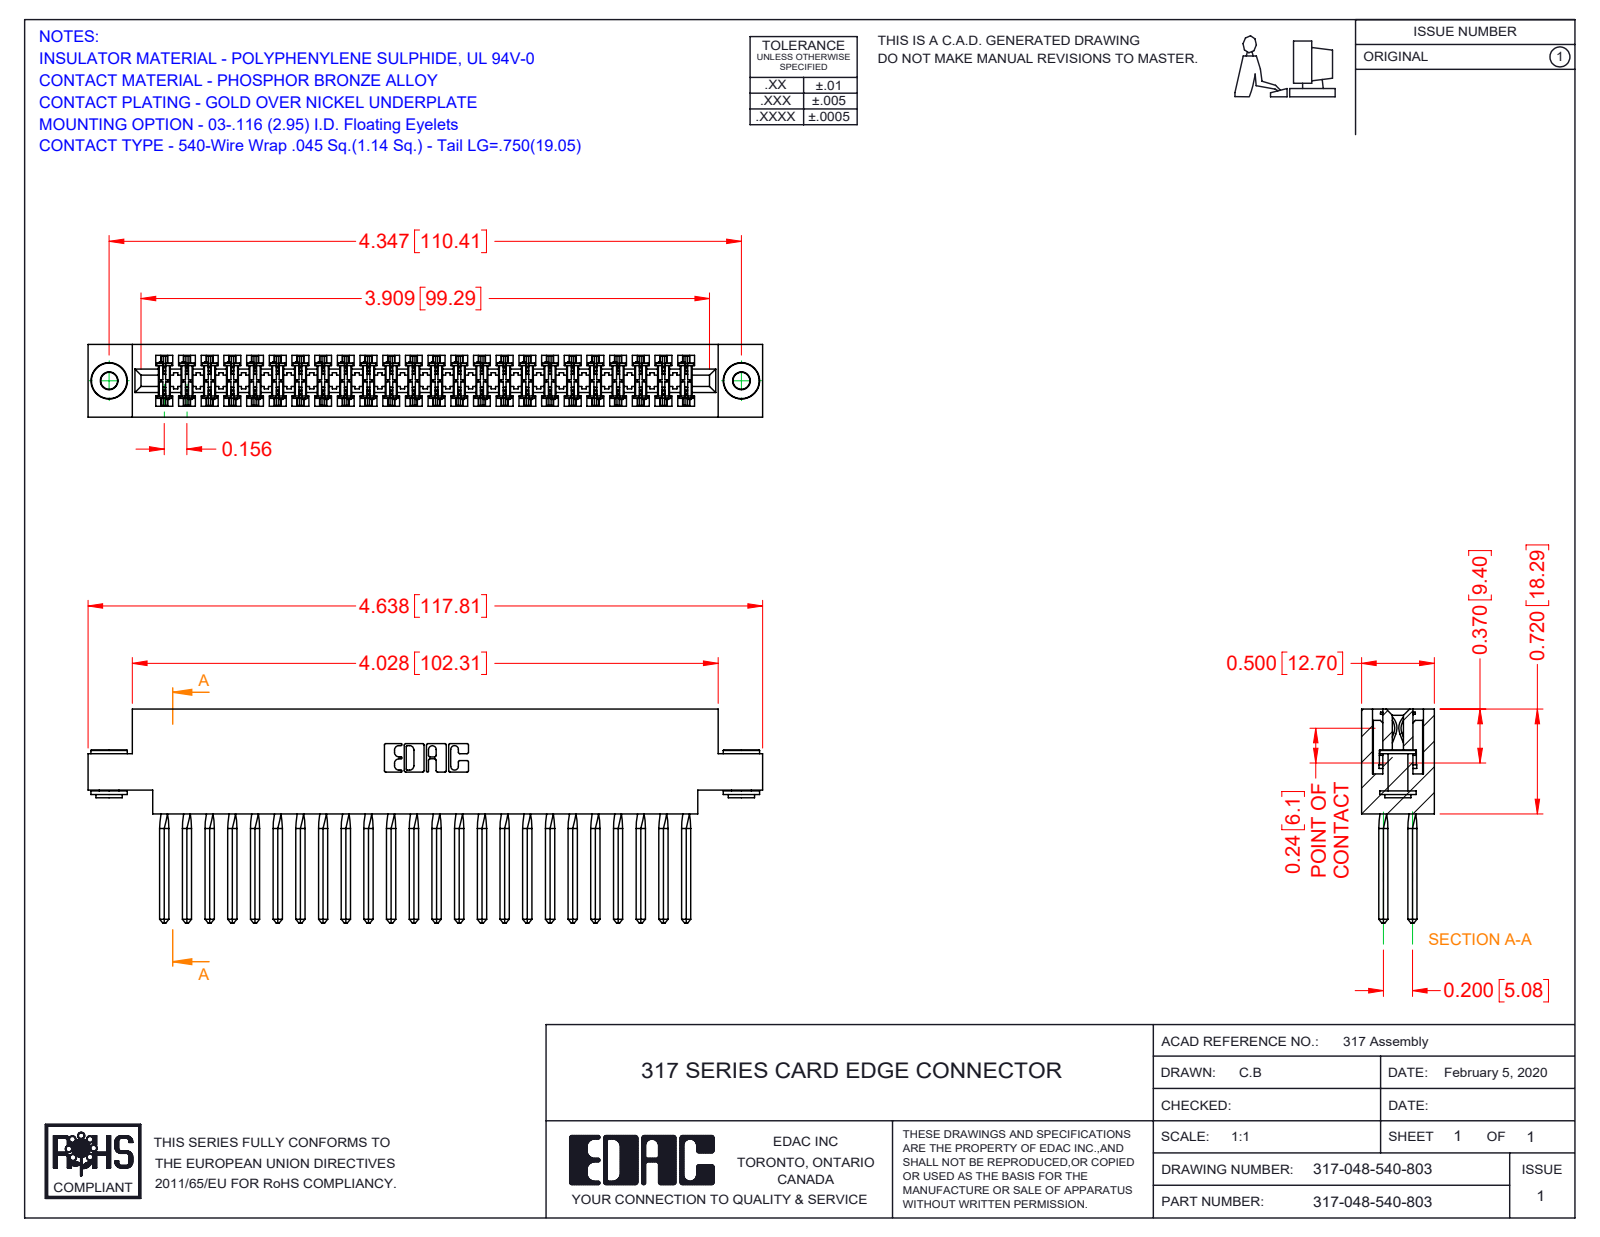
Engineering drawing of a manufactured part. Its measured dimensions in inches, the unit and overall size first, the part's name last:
Units: inches
Overall size (bounding box): 4.638 × 1.47 × 0.5
Round holes (diameter × count): ⌀0.116 ×2, ⌀0.156 ×2
Round bosses / shafts (diameter × count): ⌀0.25 ×2, ⌀0.18 ×2, ⌀0.136 ×2
Partial cylindrical surfaces — rounded edges, fillets, slot ends (radius × count): R0.015 ×96, R0.01 ×22, R0.007 ×6, R0.031 ×6, R0.026 ×3, R0.095 ×2, R0.1 ×2, R0.11 ×2
Main face-to-face distances: 0.5, 0.075, 0.425, 0.35, 0.11, 0.195, 0.094, 0.72, 0.2, 0.115
Hole centre spacings: 4.347
Volume: 1.171 in³ · Surface area: 43.61 in²
Bodies: 51 solids, 4412 faces (3572 planar, 640 cylindrical, 200 other)
Part name (STEP PRODUCT): 317 Part_.156 Dia - TH; 345-250-002_345-250-002-102; 317-048-540-803; 317-290-001_540
STEP written by: SolidWorks 2016 (CONFIG_CONTROL_DESIGN)
